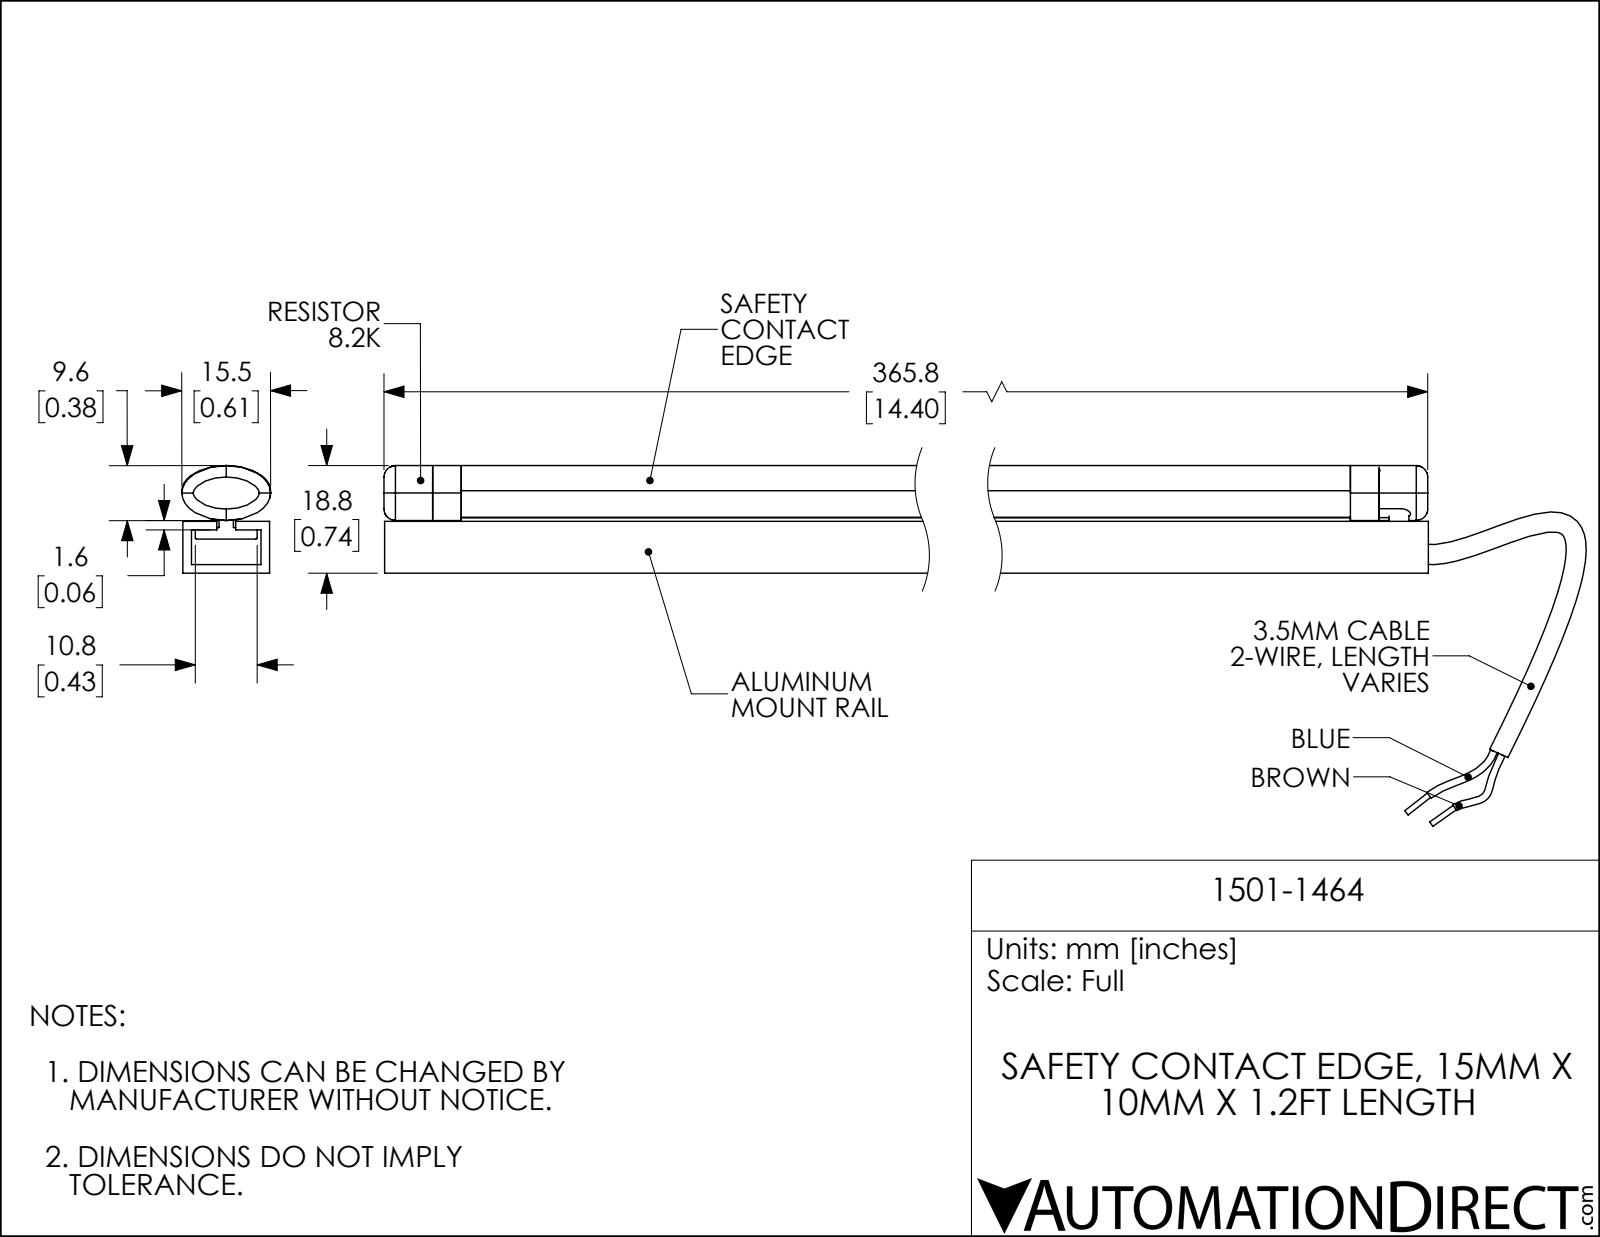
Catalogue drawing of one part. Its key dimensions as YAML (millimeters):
part_name: "1501-1464"
step_written_by: "SolidWorks 2018 (AUTOMOTIVE_DESIGN)"
units: millimeters
bodies: {solids: 7, faces: 607, planar: 129, cylindrical: 154, other: 324}
overall_size: [393.4, 63, 15.5]
volume: 58960
surface_area: 66710
round_holes:
  - {diameter: 1.2, count: 4}
round_bosses_or_shafts:
  - {diameter: 0.9, count: 2}
partial_cylinders:
  - {radius: 0.1, count: 52}
  - {radius: 0.4, count: 15}
  - {radius: 0.3, count: 10}
  - {radius: 0.2, count: 7}
  - {radius: 0.5, count: 4}
  - {radius: 13, count: 4}
  - {radius: 0.2, count: 3}
  - {radius: 1.5, count: 3}
face_to_face_distances: [1.5, 7.5, 13.6, 9, 0.4, 3.1, 5.9, 4.4, 15.1, 6]
hole_center_spacings: [5, 5, 5]
